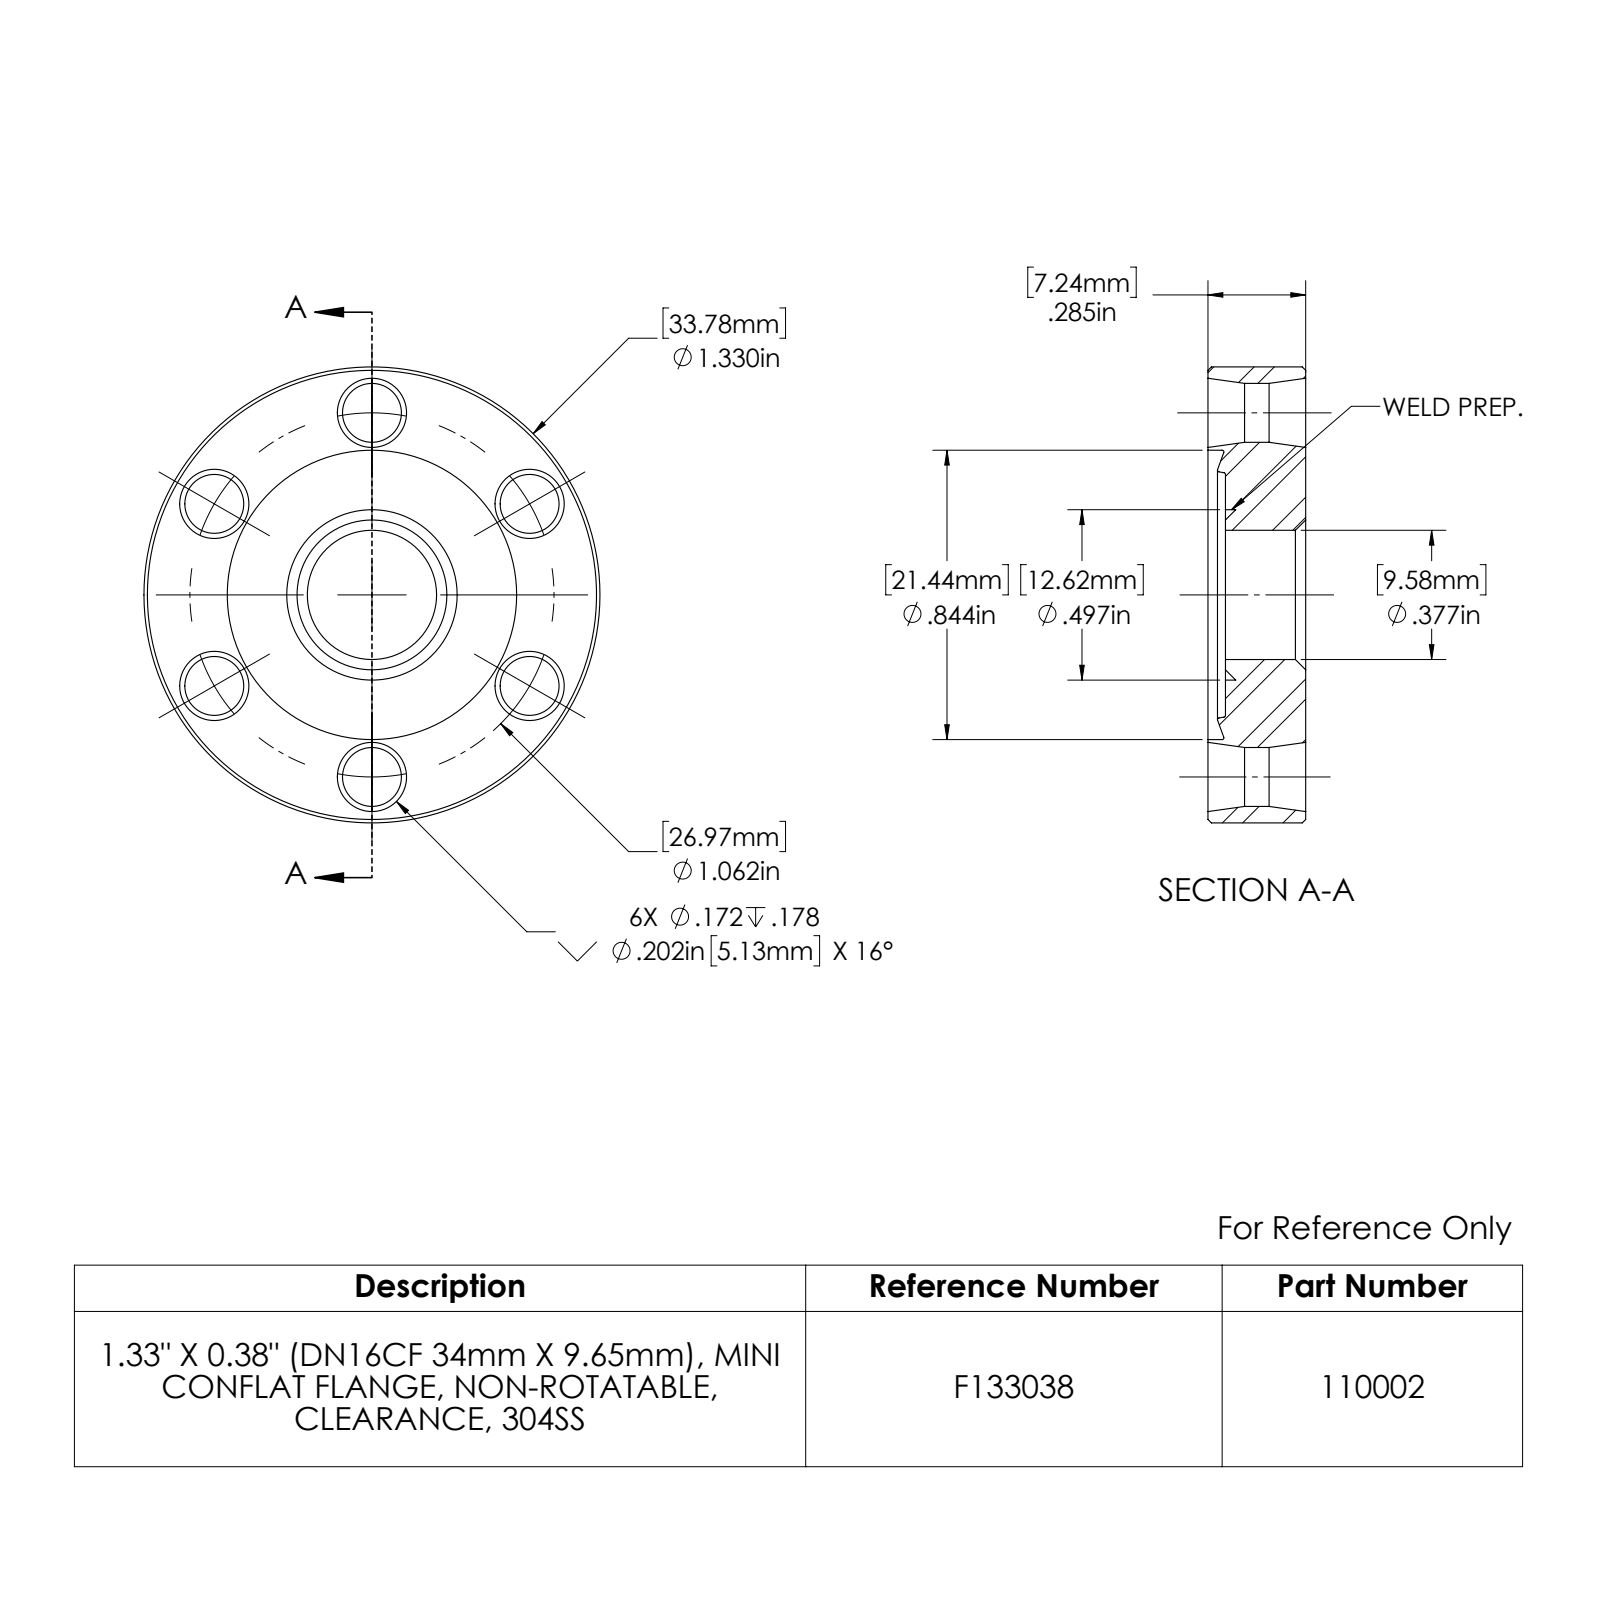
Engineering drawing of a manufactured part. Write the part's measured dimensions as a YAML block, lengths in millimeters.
part_name: "110002"
step_written_by: "SolidWorks 2022 (AUTOMOTIVE_DESIGN)"
units: millimeters
bodies: {solids: 1, faces: 66, planar: 4, cylindrical: 20, other: 42}
overall_size: [33.8, 33.8, 7.2]
volume: 4870
surface_area: 3090
round_holes:
  - {diameter: 4.4, count: 6}
  - {diameter: 9.6, count: 1}
  - {diameter: 12.6, count: 1}
  - {diameter: 21.4, count: 1}
round_bosses_or_shafts:
  - {diameter: 33.8, count: 1}
face_to_face_distances: [7.2, 1.3, 5.9]
hole_center_spacings: [13.5, 23.4, 13.5, 27, 27]
